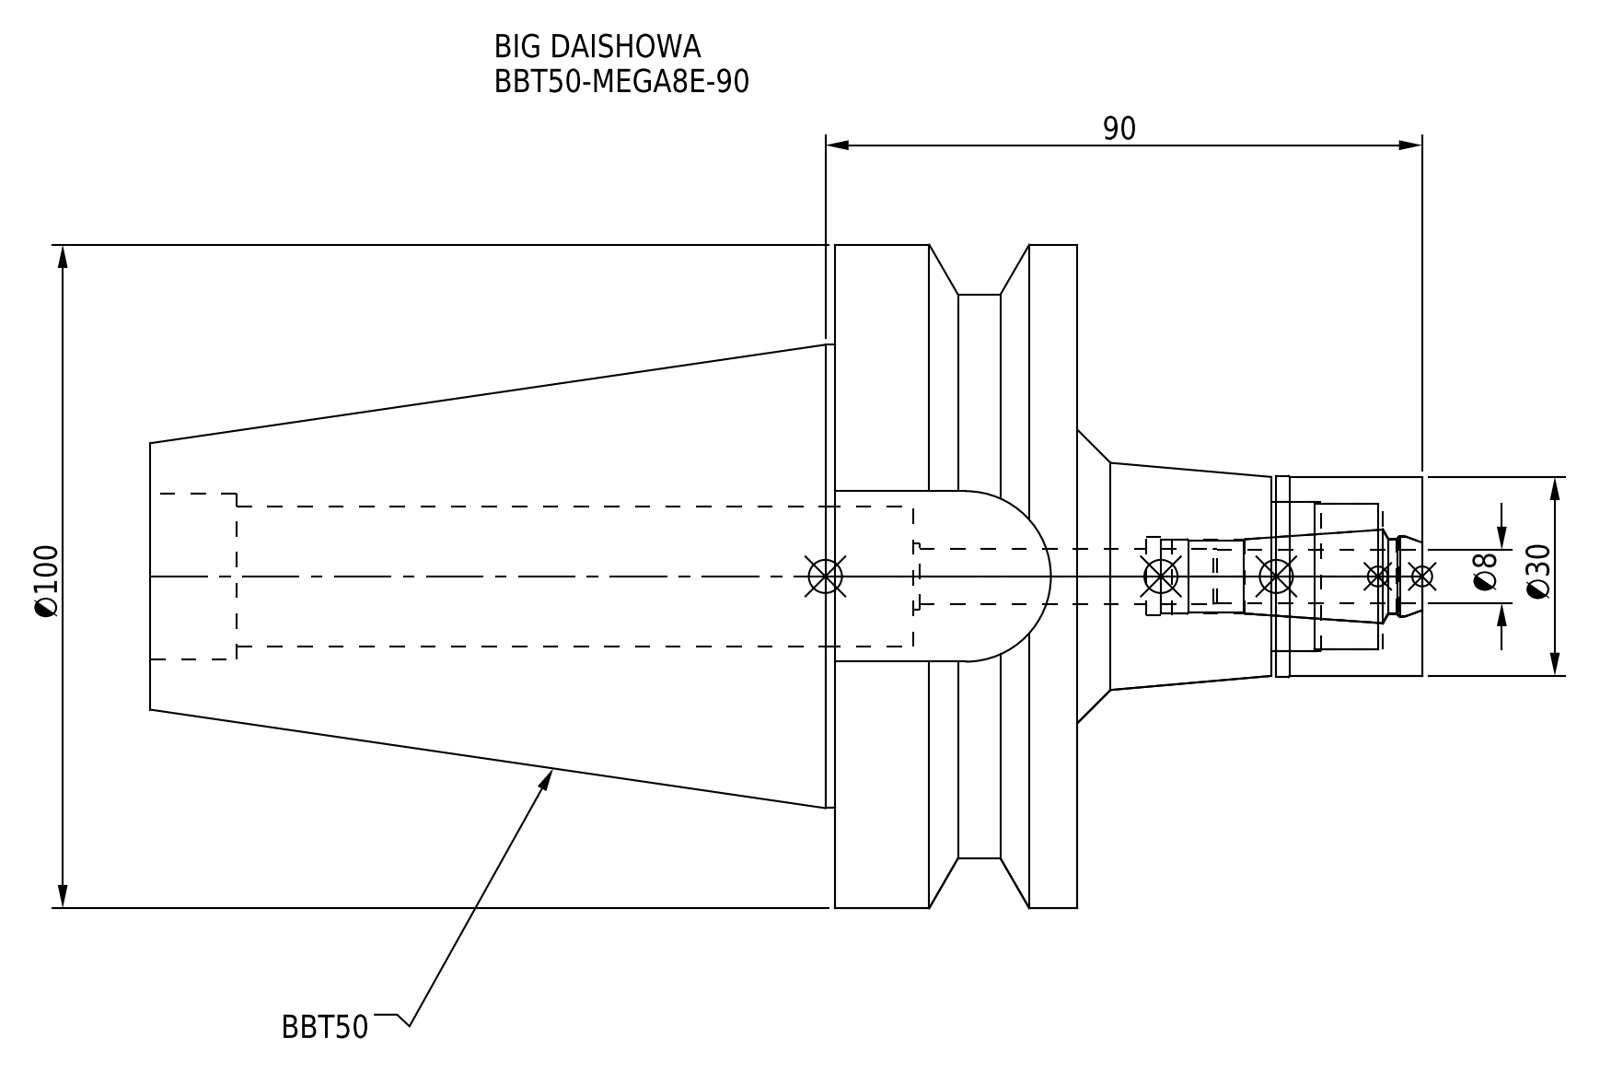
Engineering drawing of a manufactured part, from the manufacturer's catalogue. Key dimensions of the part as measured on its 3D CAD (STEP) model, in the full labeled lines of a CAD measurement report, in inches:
Part name (STEP PRODUCT): DXF_TEMP_ASSY_ASM_4_ASM.stp; BBT50-MEGA8E-90_1.stp; BBT50-MEGA8E-90; BBT50ME08090-080_ASM.stp (+3 more)
STEP written by: SolidWorks 2019 (CONFIG_CONTROL_DESIGN)
Units: inches
Bodies: 2 solids, 81 faces (21 planar, 40 cylindrical, 20 other)
Overall size (bounding box): 7.551 × 3.937 × 3.937
Volume: 29.98 in³ · Surface area: 98.5 in²
Round holes (diameter × count): ⌀0.331 ×1, ⌀0.394 ×1, ⌀0.441 ×1, ⌀0.449 ×1, ⌀0.465 ×1, ⌀0.484 ×1, ⌀0.835 ×1, ⌀0.866 ×1, ⌀0.886 ×1, ⌀0.984 ×1
Round bosses / shafts (diameter × count): ⌀3.937 ×1, ⌀3.346 ×1, ⌀2.75 ×1, ⌀1.193 ×1, ⌀1.181 ×1
Partial cylindrical surfaces — rounded edges, fillets, slot ends (radius × count): R0.506 ×1
Main face-to-face distances: 1.437, 2.787, 5.504, 4.067, 2.047, 3.484, 7.551, 1.012, 0.866, 1.181
